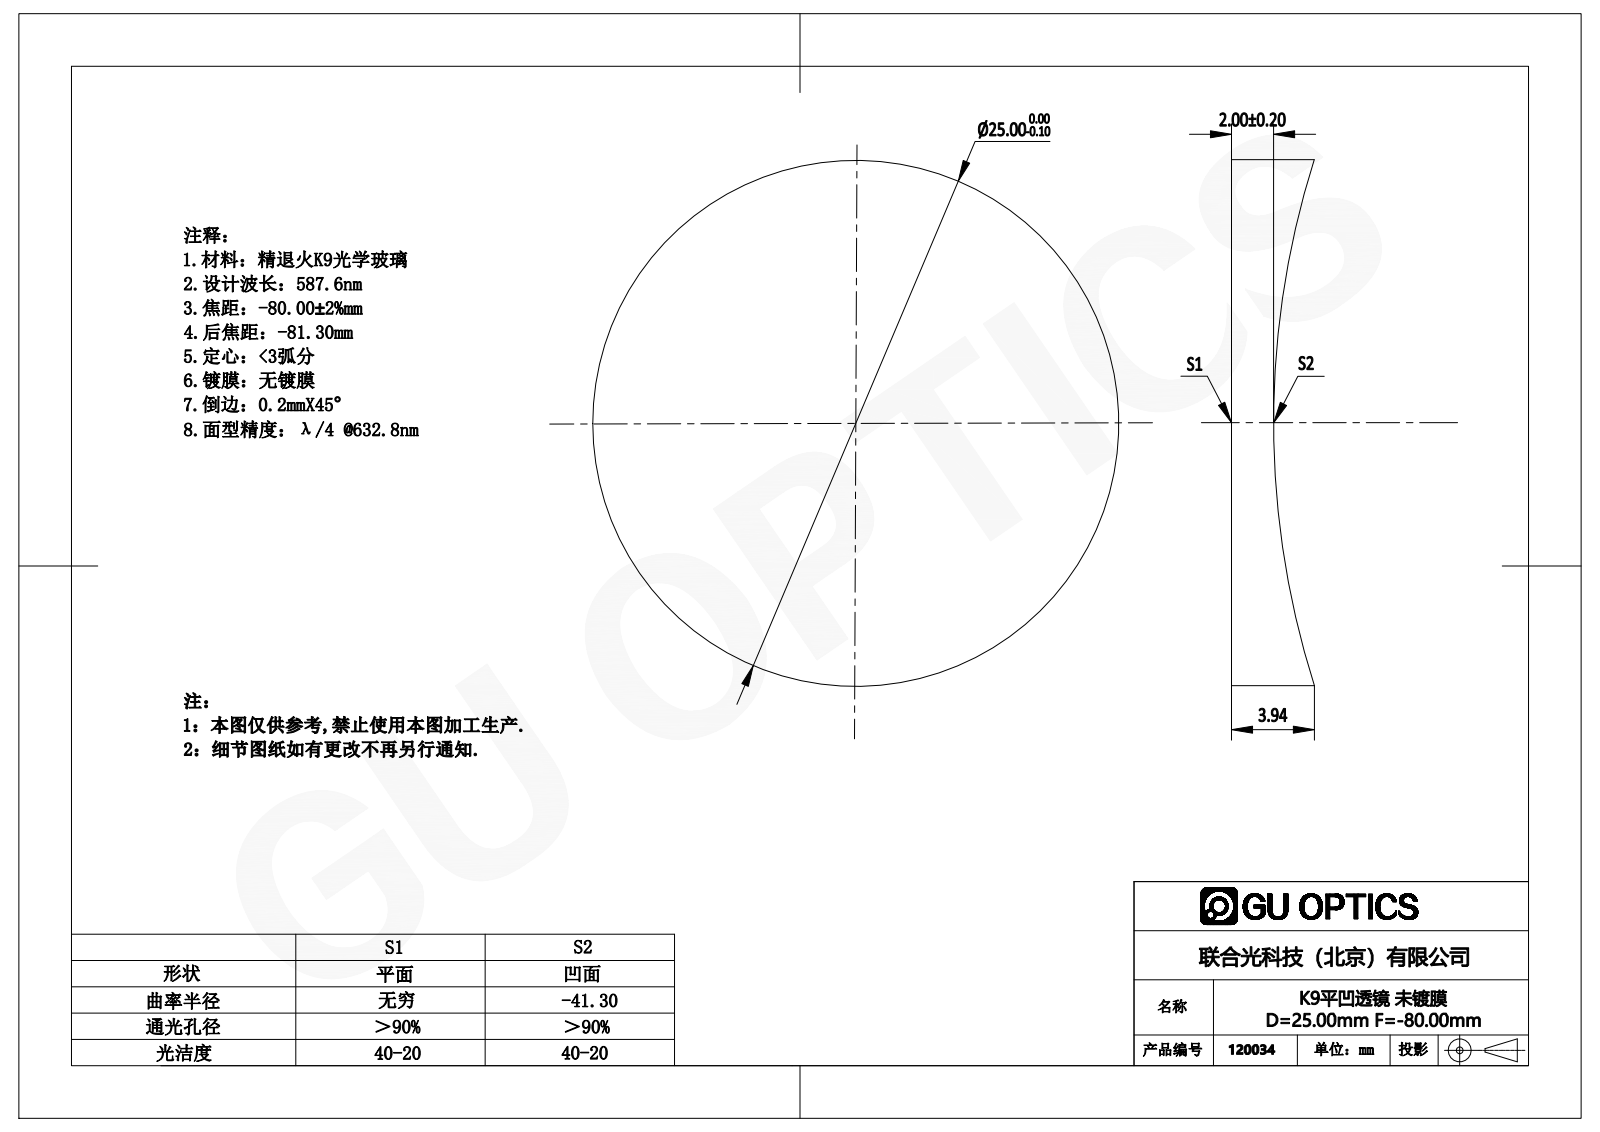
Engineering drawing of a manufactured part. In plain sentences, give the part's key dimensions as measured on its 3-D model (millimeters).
The part is named "120034". Its 3-D file was written by "SolidWorks 2016 (AUTOMOTIVE_DESIGN)". It is 1 solid with 5 faces: 1 planar, 2 cylindrical and 2 other. Overall it measures 25 by 25 by 3.93 millimeters. Its volume is 1 452 cubic millimeters and its surface area 1 302 square millimeters. Round bosses or shafts: 1 of diameter 25.
